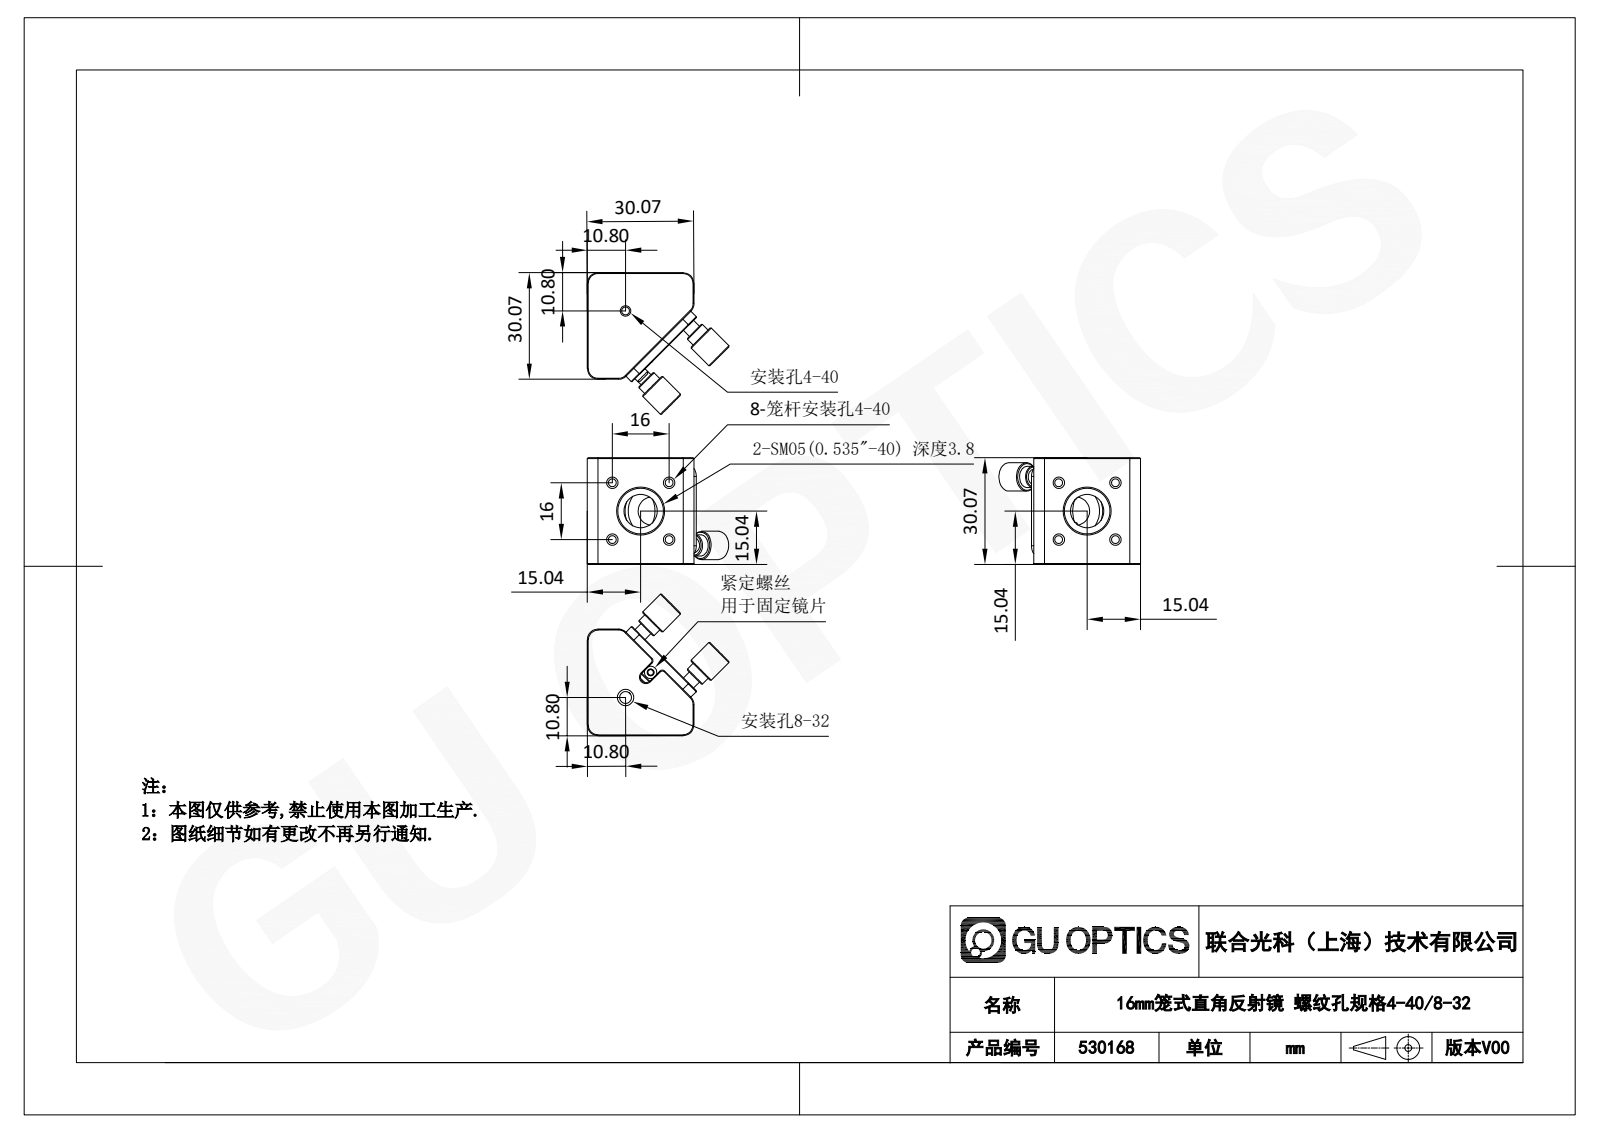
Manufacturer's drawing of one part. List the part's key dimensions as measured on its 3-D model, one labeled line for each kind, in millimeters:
Part name (STEP PRODUCT): 530168
STEP written by: SolidWorks 2020 (CONFIG_CONTROL_DESIGN)
Units: millimetres
Bodies: 22 solids, 398 faces (170 planar, 93 cylindrical, 135 other)
Overall size (bounding box): 40.62 × 40.62 × 30.07
Volume: 16 724 mm³ · Surface area: 11 889 mm²
Round holes (diameter × count): ⌀2.26 ×9, ⌀3.5 ×6, ⌀3.75 ×5, ⌀2.9 ×4, ⌀2.99 ×3, ⌀9.5 ×2, ⌀12.95 ×2, ⌀13.95 ×2, ⌀2.5 ×1, ⌀3.45 ×1, ⌀4.6 ×1, ⌀11.94 ×1
Round bosses / shafts (diameter × count): ⌀1.5 ×6, ⌀4 ×3, ⌀8 ×2, ⌀6 ×2, ⌀3 ×2, ⌀16.5 ×1, ⌀2 ×1
Partial cylindrical surfaces — rounded edges, fillets, slot ends (radius × count): R0.78 ×12, R3 ×9, R1 ×4, R3.17 ×4, R0.3 ×2, R4 ×2, R1.59 ×1, R1.75 ×1
Main face-to-face distances: 30.08, 0.75, 26.65, 10.62, 3, 7.62, 1.34, 28.74, 27.4, 2.09
Hole centre spacings: 11.31, 16, 4.85, 14.45, 22.63, 13.64, 19.3, 19.9
